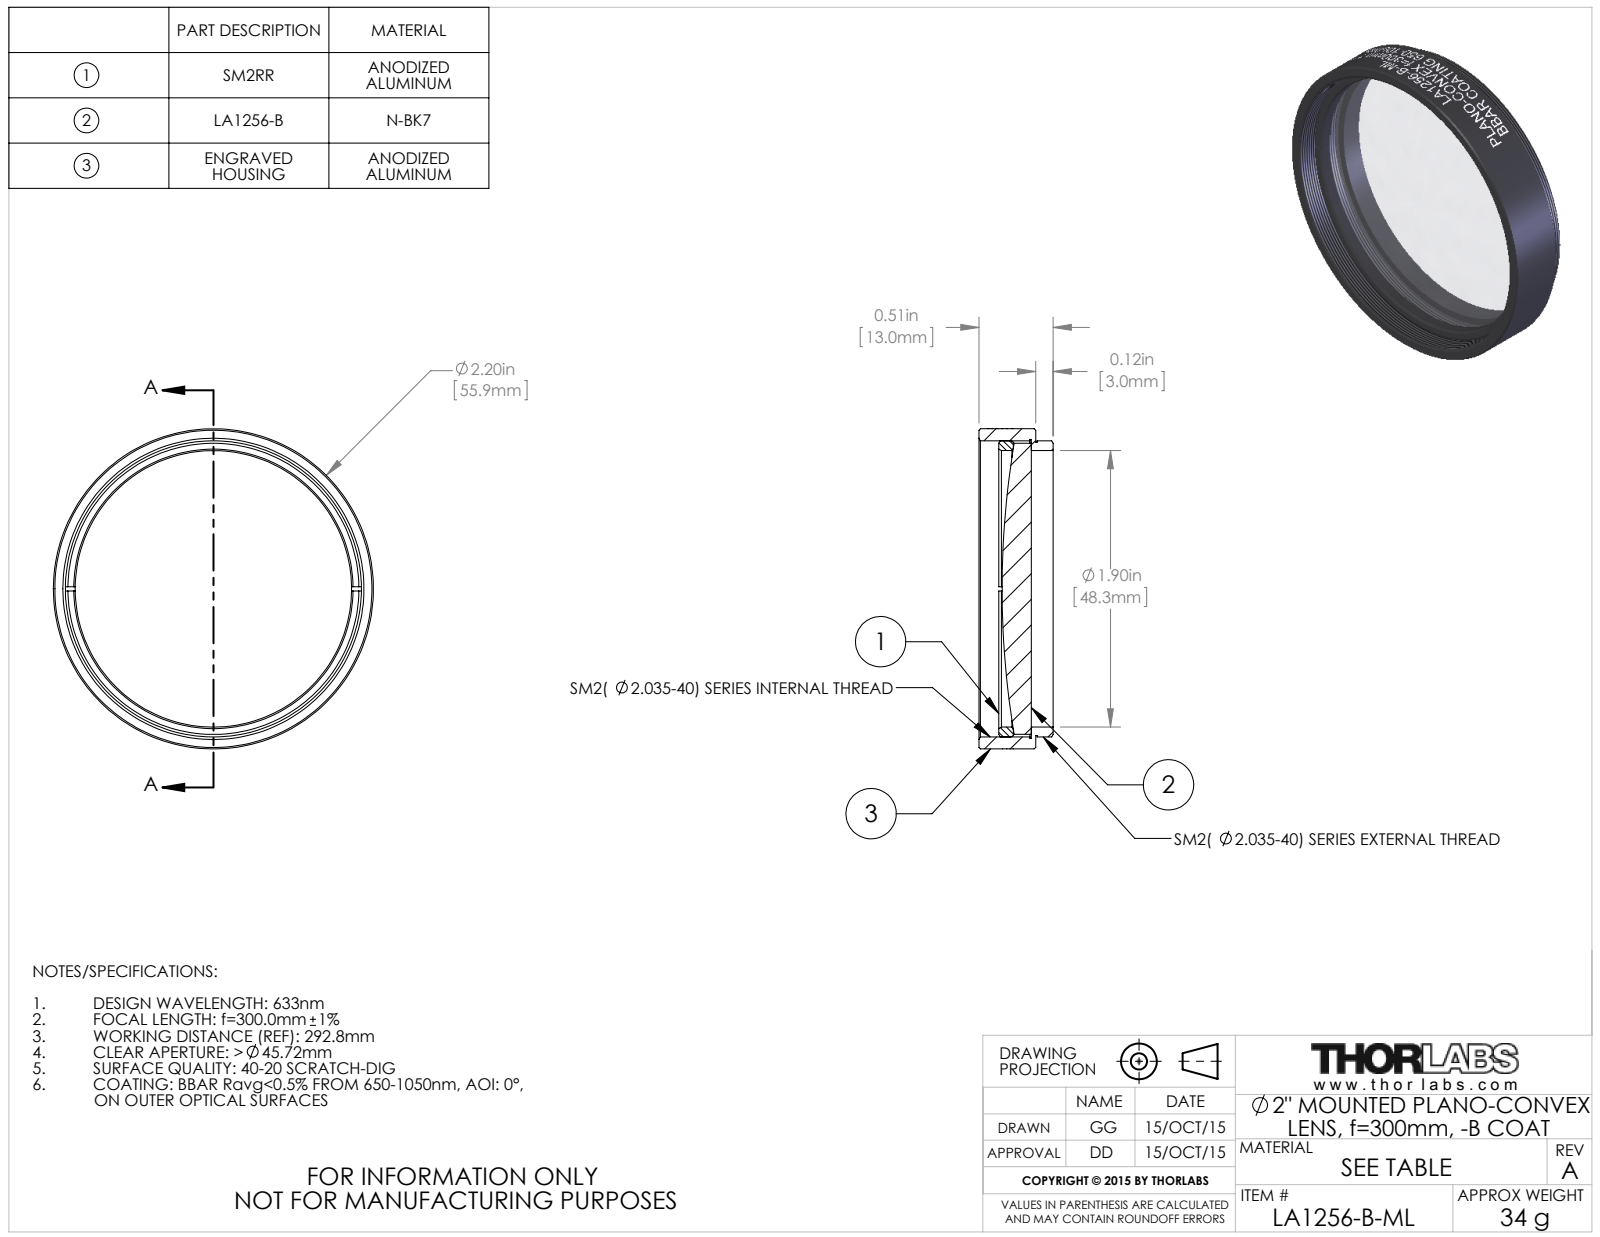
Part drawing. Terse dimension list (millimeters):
name: TTN039540-E0W
written by: SolidWorks 2014 (CONFIG_CONTROL_DESIGN)
unit: mm
bodies: 3 solids, 145 faces (16 planar, 109 cylindrical, 20 other)
size: 55.9 × 55.9 × 13
volume: 13 300 mm³; area: 11 360 mm²
holes: 1× ⌀48.3, 1× ⌀52.2
bosses: 1× ⌀55.9, 1× ⌀51.7, 1× ⌀51.2, 1× ⌀50.8
face distances: 0.8, 9.9, 9.1, 3, 3.8, 13, 7, 3.9, 3.1, 6
